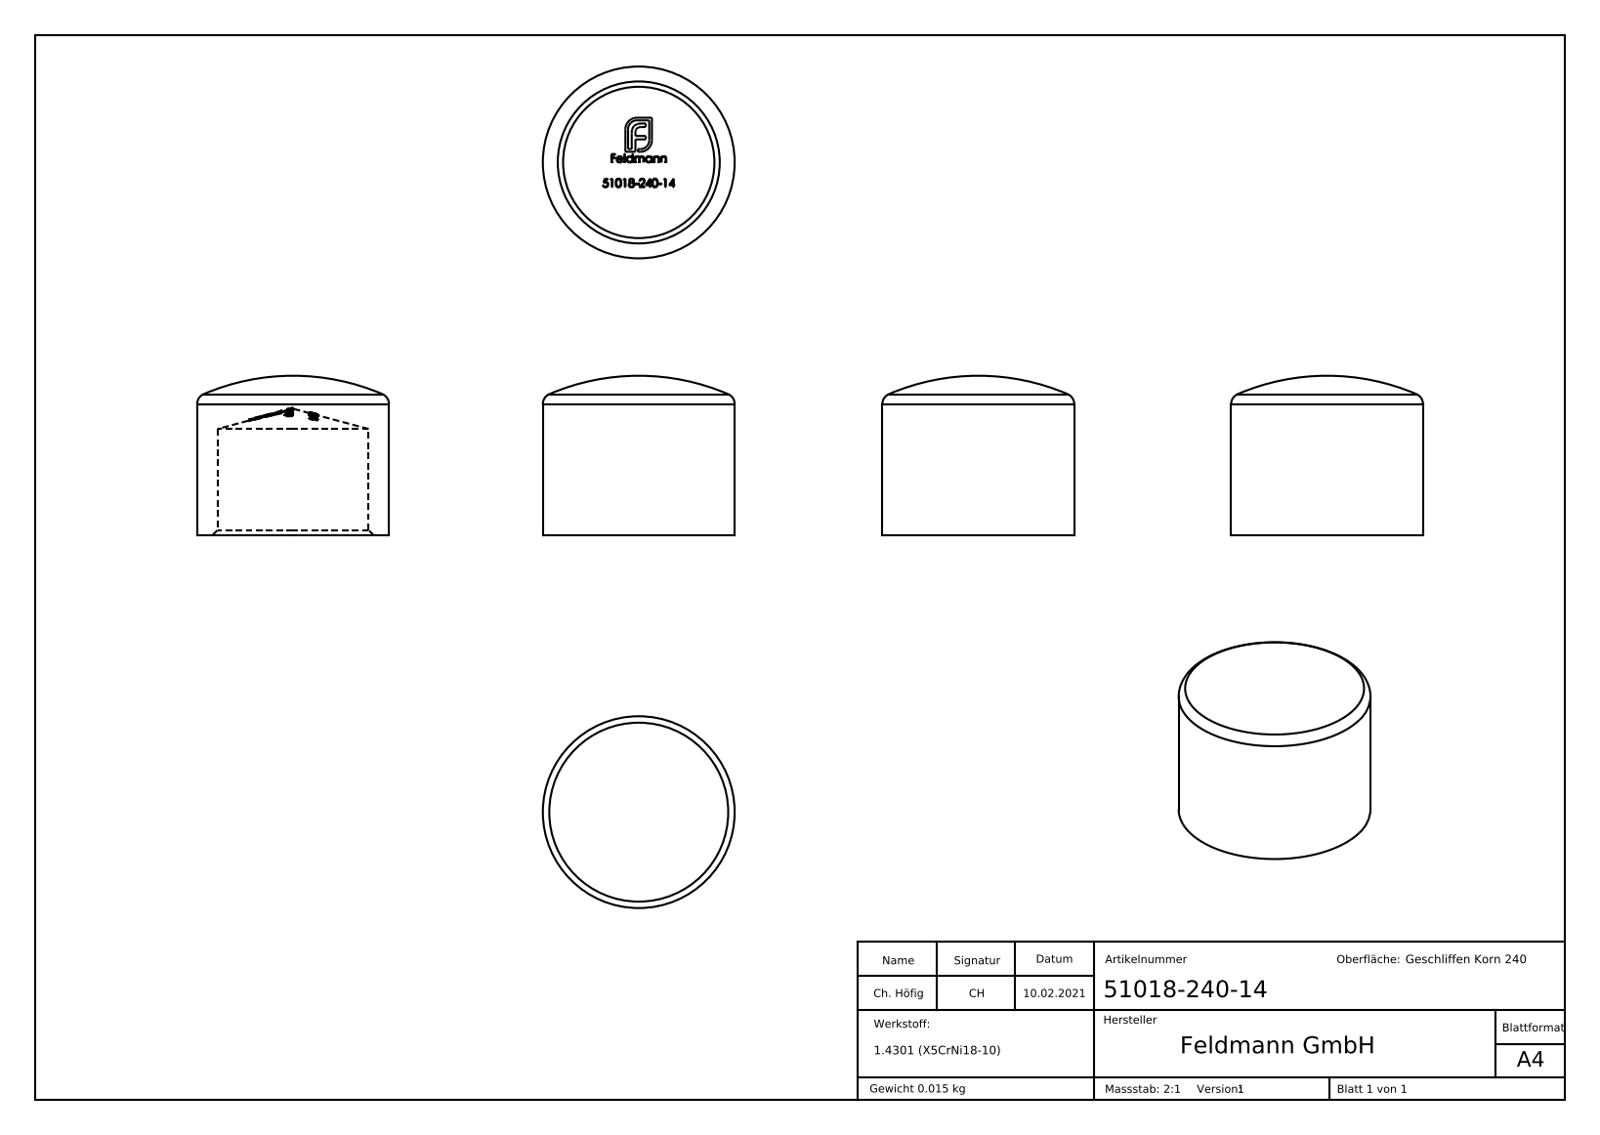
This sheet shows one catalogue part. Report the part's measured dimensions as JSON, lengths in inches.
{"part_name": "51018-240-14", "step_written_by": "SolidWorks 2018 (CONFIG_CONTROL_DESIGN)", "units": "inches", "bodies": {"solids": 1, "faces": 305, "planar": 139, "cylindrical": 4, "other": 162}, "overall_size": [0.709, 0.709, 0.591], "volume_in3": 0.114, "surface_area_in2": 2.629, "round_holes": [[0.559, 1]], "round_bosses_or_shafts": [[0.709, 1]], "face_to_face_distances": [0.088, 0.074, 0.078, 0.048, 0.051, 0.098, 0.013, 0.059, 0.087, 0.049]}
